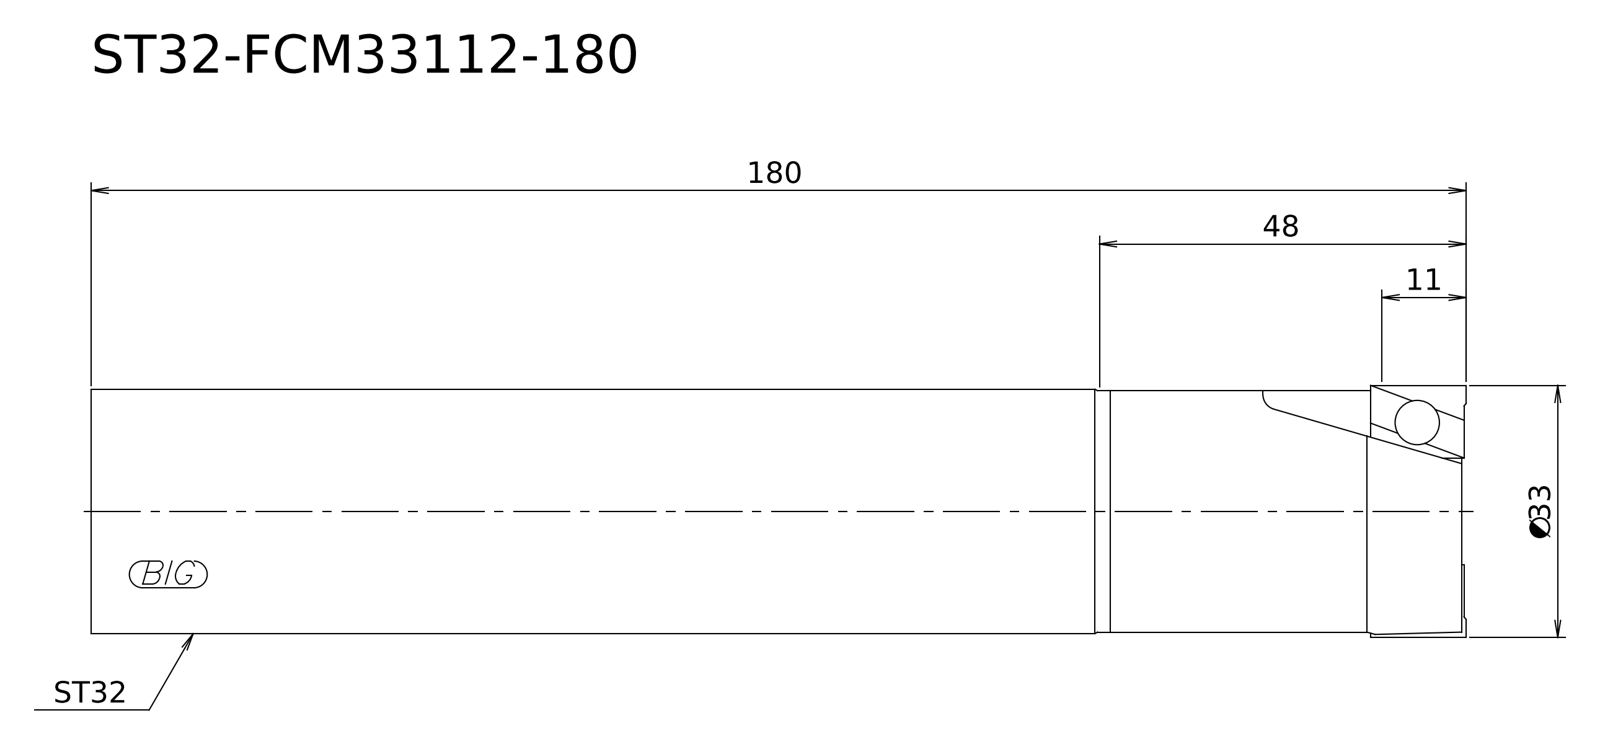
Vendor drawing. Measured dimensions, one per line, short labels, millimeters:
written by: Kubotek KeyCreator V8.5.1 (14335) (CONFIG_CONTROL_DESIGN)
unit: mm
bodies: 1 solid, 7 faces (3 planar, 3 cylindrical, 1 other)
size: 180 × 33 × 33
volume: 144 686 mm³; area: 19 826 mm²
bosses: 1× ⌀33, 1× ⌀32, 1× ⌀31.6
face distances: 180, 12.51, 167.49
